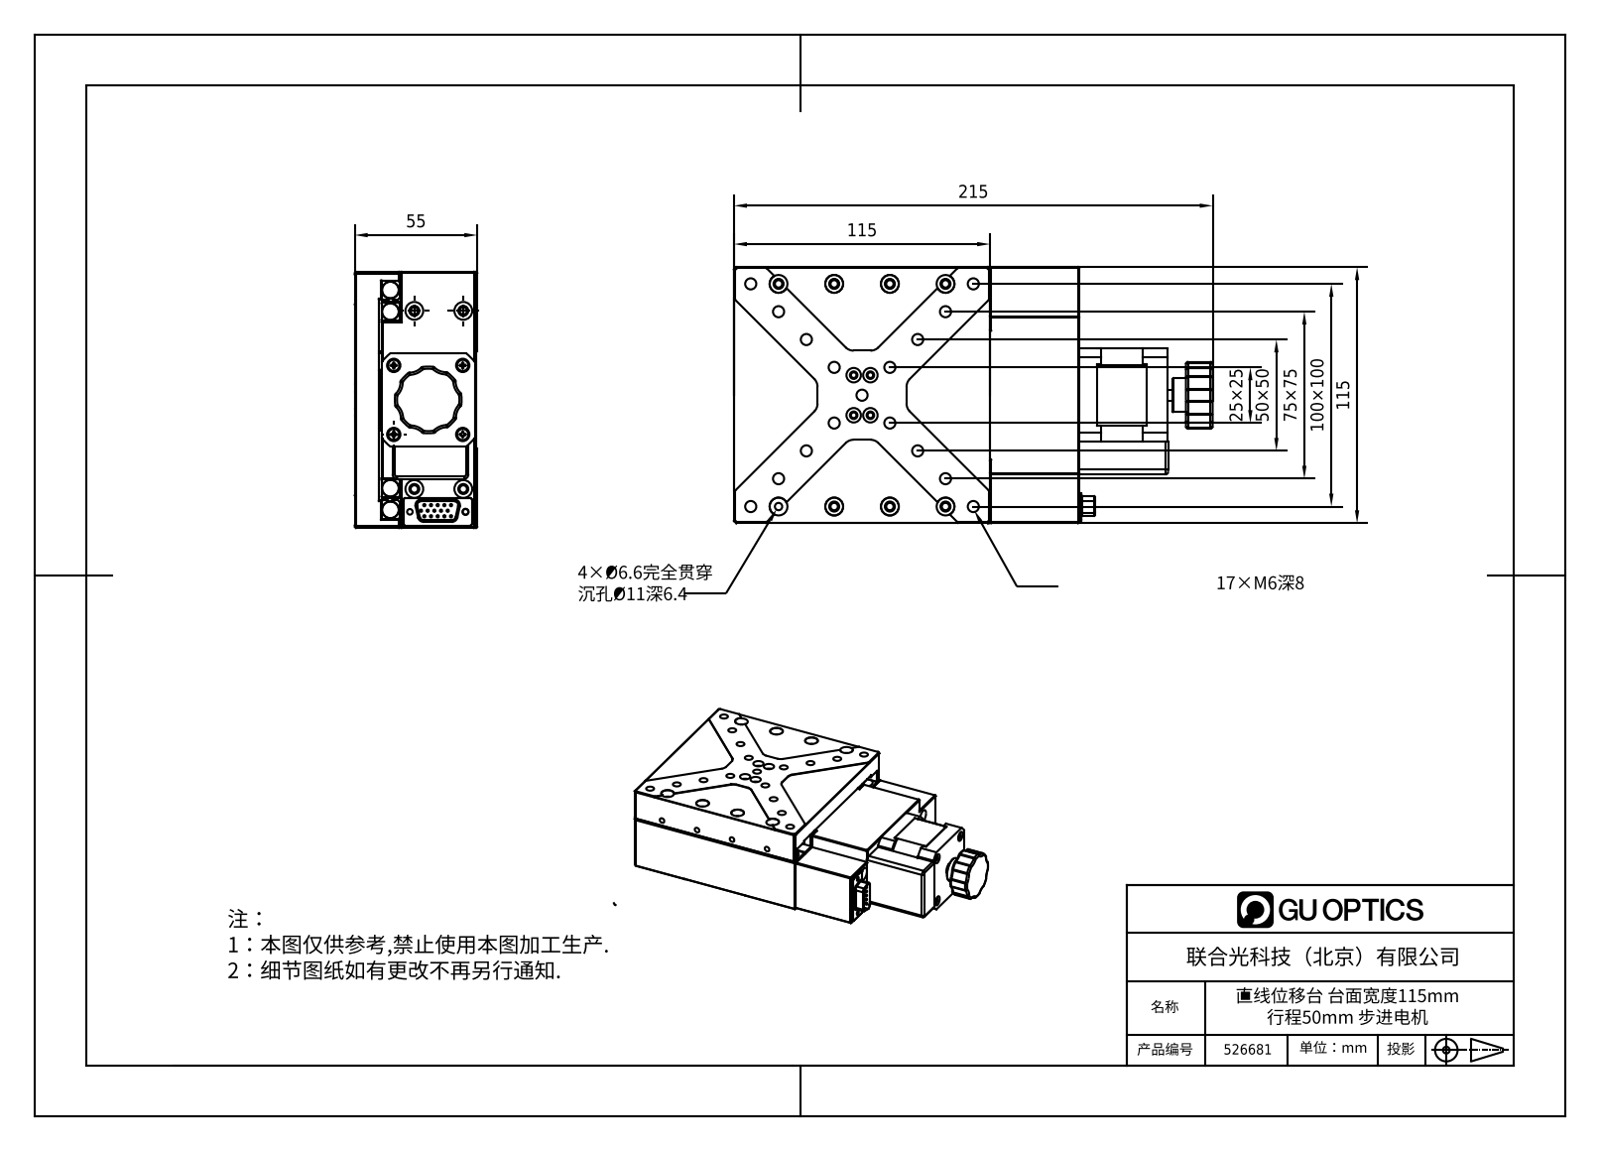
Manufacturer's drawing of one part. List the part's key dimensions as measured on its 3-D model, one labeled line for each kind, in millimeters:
Part name (STEP PRODUCT): FMS115R-50
STEP written by: SolidWorks 2020 (AUTOMOTIVE_DESIGN)
Units: millimetres
Bodies: 0 solids, 3434 faces (1646 planar, 915 cylindrical, 873 other)
Overall size (bounding box): 215 × 115 × 55
Round holes (diameter × count): ⌀3.3 ×25, ⌀6 ×21, ⌀2.5 ×20, ⌀5 ×19, ⌀0.8 ×15, ⌀4.5 ×12, ⌀8 ×12, ⌀3.4 ×10, ⌀1.5 ×9, ⌀2.4 ×8, ⌀6.5 ×8, ⌀2 ×4
Round bosses / shafts (diameter × count): ⌀3 ×29, ⌀1 ×15, ⌀5 ×4, ⌀1.5 ×4, ⌀3.2 ×2, ⌀22 ×1, ⌀17 ×1, ⌀16 ×1
Partial cylindrical surfaces — rounded edges, fillets, slot ends (radius × count): R1 ×45, R2 ×29, R5 ×22, R0.5 ×20, R0.1 ×12, R3 ×12, R1.5 ×8, R6 ×8
Main face-to-face distances: 1, 43.7, 115, 43, 10.7, 40, 44, 11, 54.7, 8
Hole centre spacings: 25, 27.31, 92.44, 50, 3, 2.92, 5.15, 5.83
